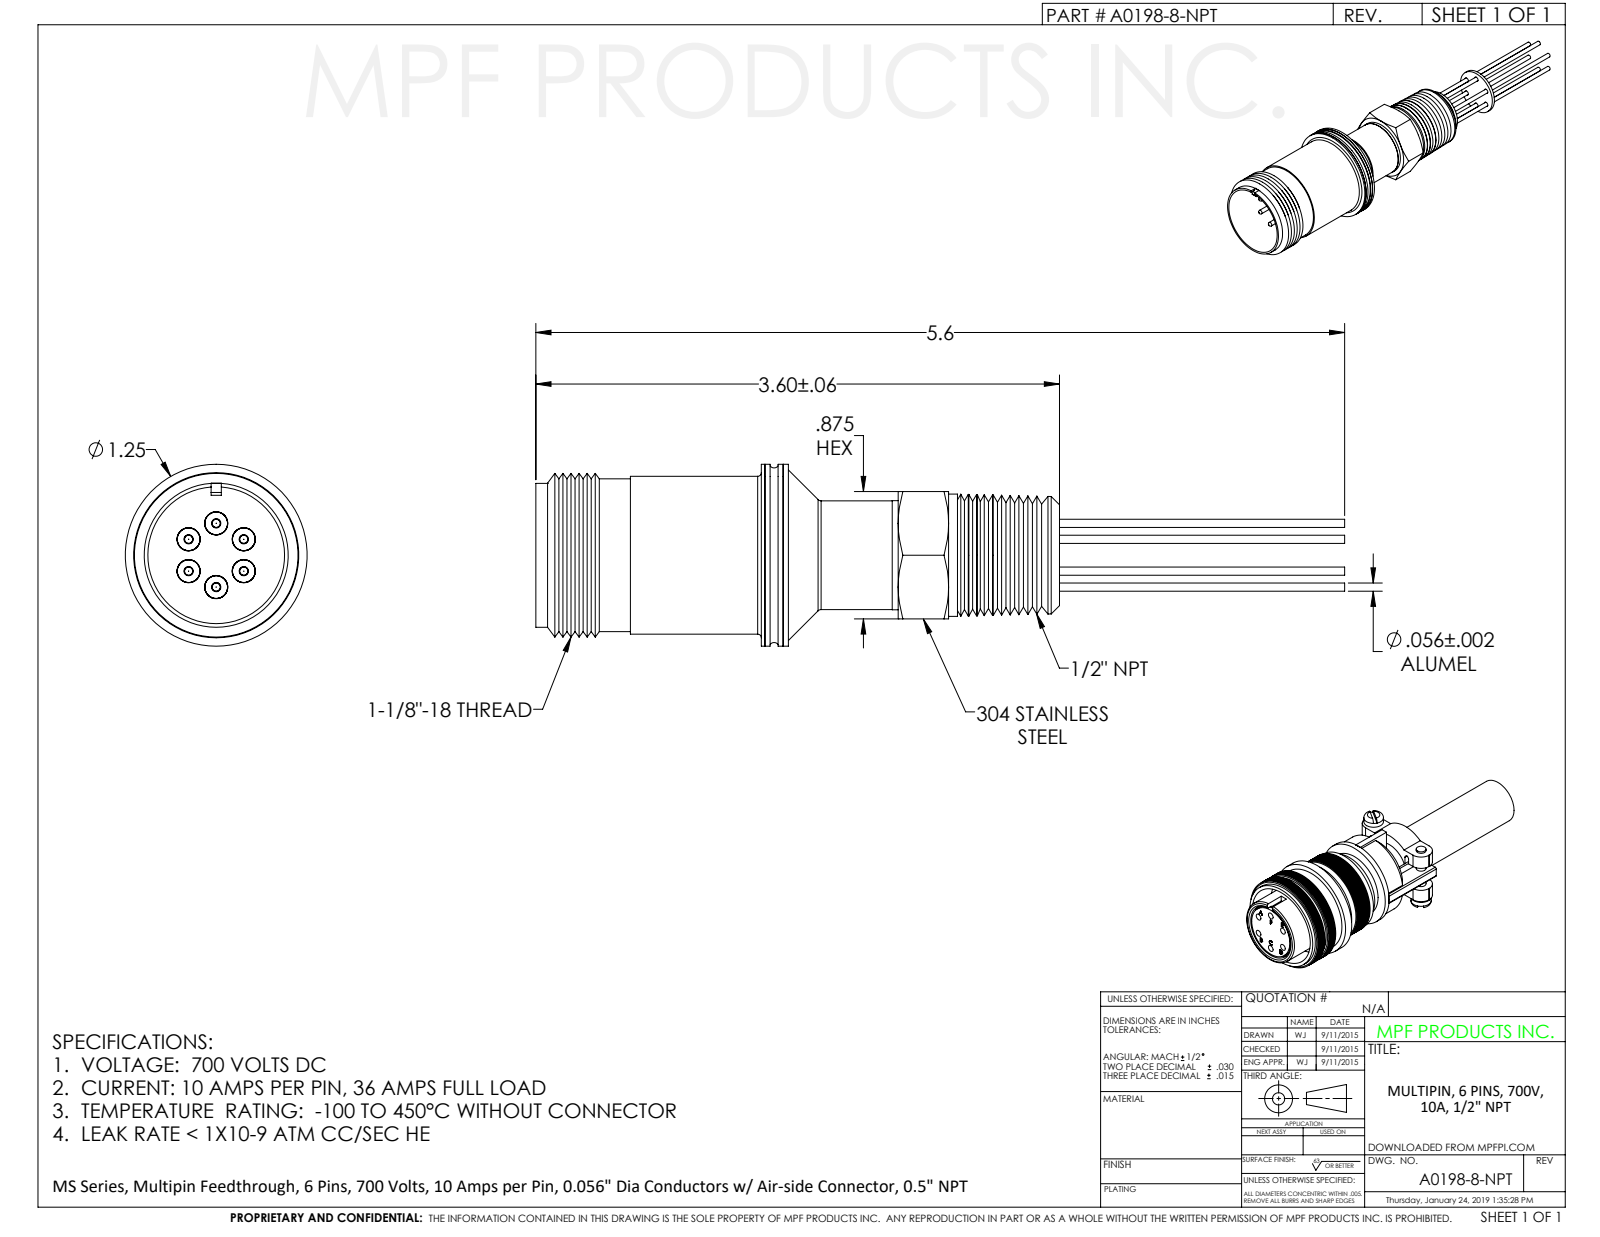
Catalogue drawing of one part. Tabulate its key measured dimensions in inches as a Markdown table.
| quantity | value |
| --- | --- |
| part name | A0198-8-NPT |
| STEP written by | SolidWorks 2012 (CONFIG_CONTROL_DESIGN) |
| units | inches |
| bodies | 1 solid, 311 faces (70 planar, 120 cylindrical, 121 other) |
| overall size | 5.595 × 1.25 × 1.25 |
| volume | 0.92 in³ |
| surface area | 36.62 in² |
| round holes (diameter × count) | 0.625 × 1, 0.675 × 1, 0.94 × 1, 0.97 × 1, 1.035 × 1 |
| round bosses / shafts (diameter × count) | 0.187 × 6, 0.17 × 6, 0.056 × 6, 1.25 × 1, 1.085 × 1, 1.05 × 1, 1.02 × 1, 1 × 1 |
| main face-to-face distances | 0.05, 0.15, 0.04, 2.479, 0.875, 3.223, 3.263, 3.173, 3.213, 0.04 |
